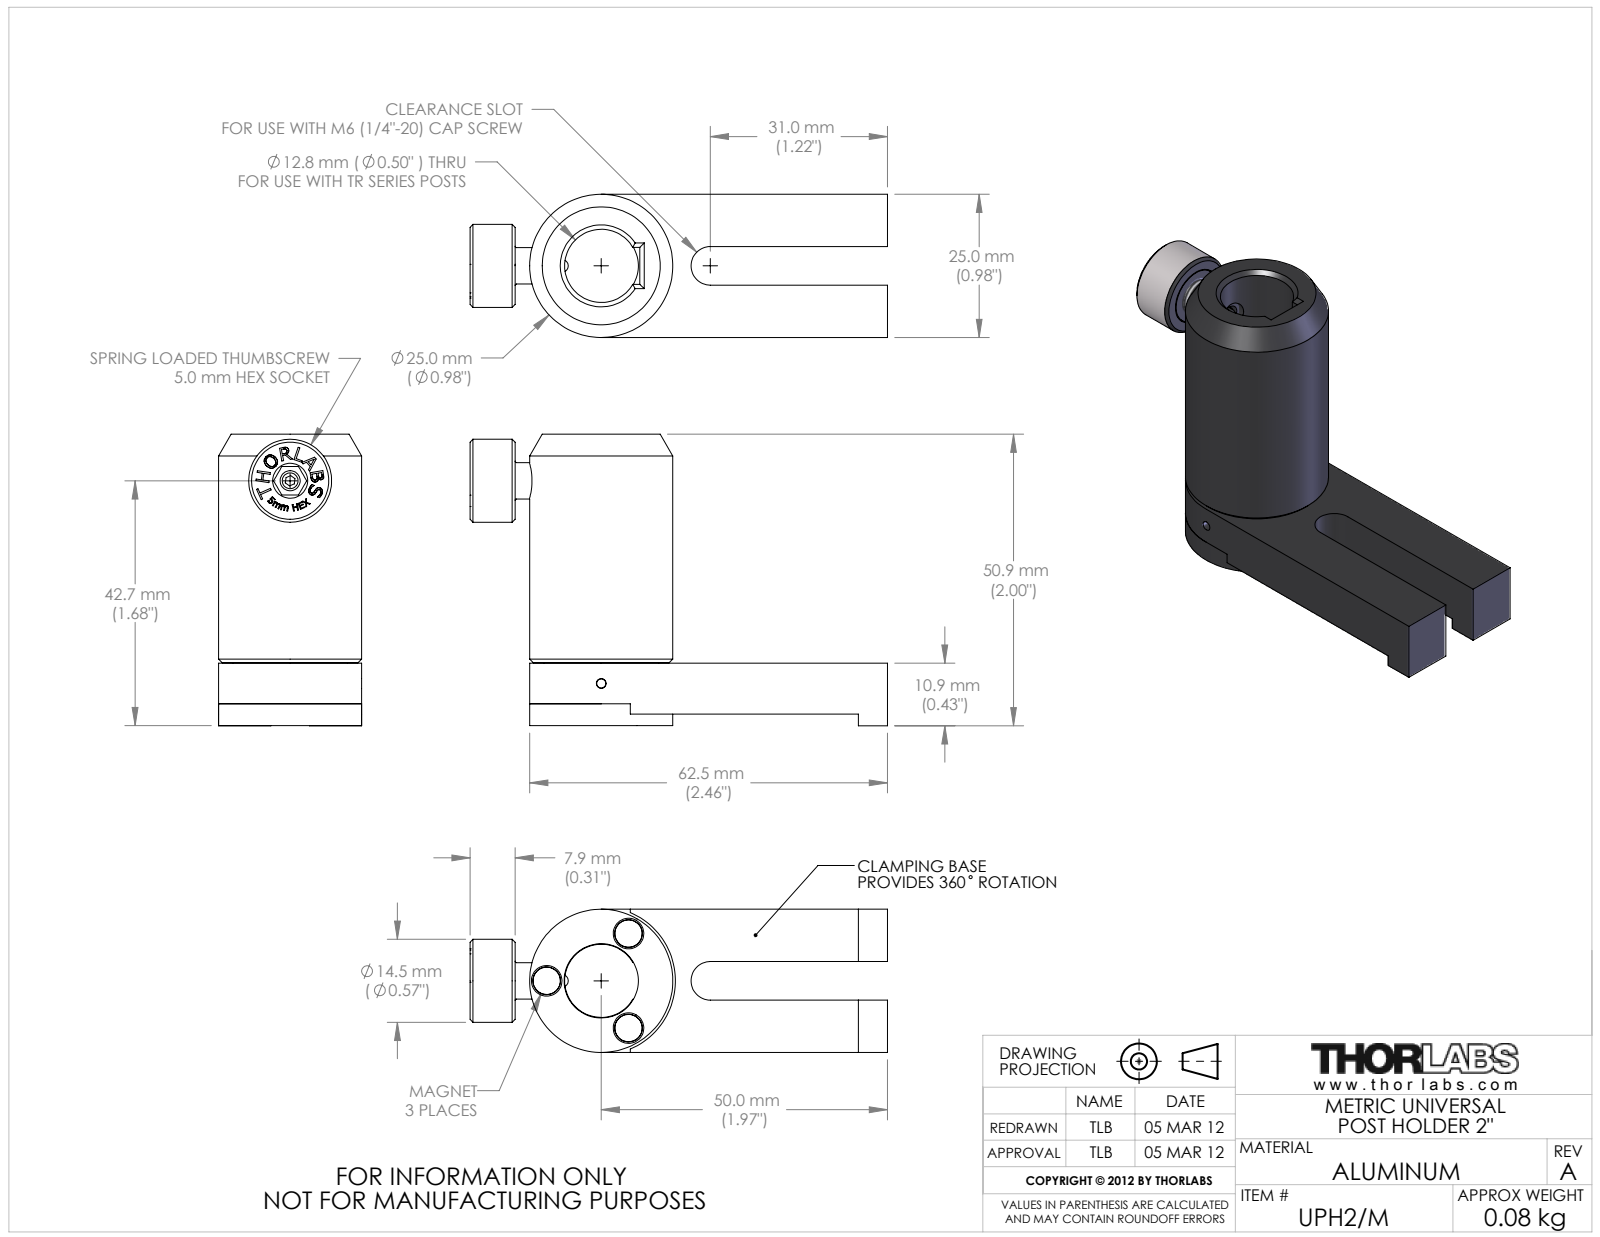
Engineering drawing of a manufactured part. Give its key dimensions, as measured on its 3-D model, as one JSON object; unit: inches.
{"part_name": "21064-E0W", "step_written_by": "SolidWorks 2011 (AUTOMOTIVE_DESIGN)", "units": "inches", "bodies": {"solids": 10, "faces": 436, "planar": 211, "cylindrical": 84, "other": 141}, "overall_size": [2.871, 2.004, 0.984], "volume_in3": 1.59, "surface_area_in2": 21.88, "round_holes": [[0.19, 3], [0.063, 1], [0.067, 1], [0.07, 1], [0.084, 1], [0.1, 1], [0.125, 1], [0.138, 1], [0.201, 1], [0.4, 1], [0.503, 1], [0.51, 1]], "round_bosses_or_shafts": [[0.187, 3], [0.984, 1], [0.79, 1], [0.7, 1], [0.68, 1], [0.57, 1], [0.39, 1], [0.25, 1]], "partial_cylinders_radius": [[0.133, 1], [0.51, 1]], "face_to_face_distances": [0.35, 0.359, 0.625, 0.984, 0.072, 0.278, 0.078, 0.15, 0.428, 0.265], "hole_center_spacings": [0.65, 0.375, 0.375]}
